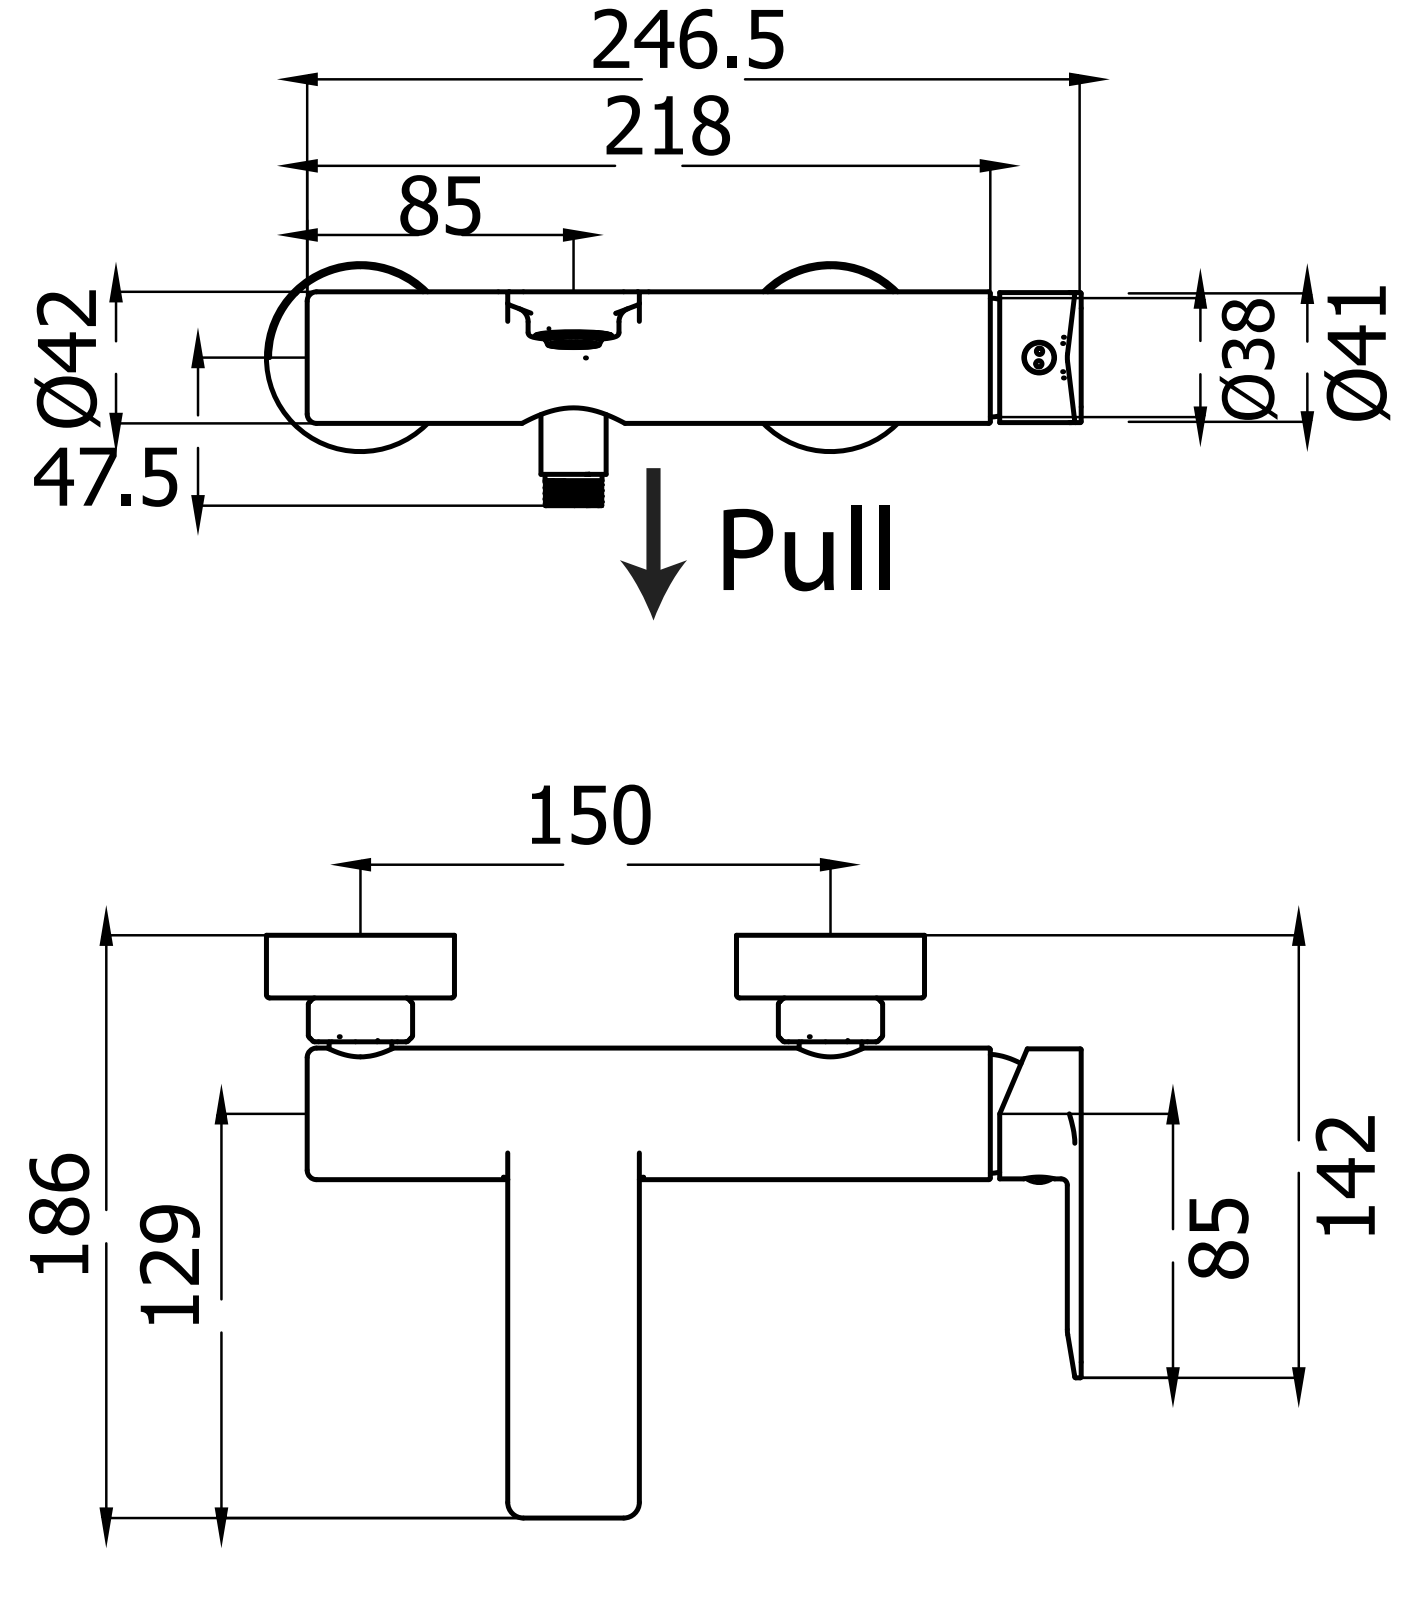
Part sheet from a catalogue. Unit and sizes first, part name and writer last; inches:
Units: inches
Overall size (bounding box): 10.217 × 7.323 × 3.042
Round holes (diameter × count): ⌀0.02 ×317, ⌀0.205 ×3, ⌀0.748 ×3, ⌀0.827 ×3, ⌀0.079 ×2, ⌀0.236 ×2, ⌀0.276 ×2, ⌀0.354 ×2, ⌀0.661 ×2, ⌀0.736 ×2, ⌀0.839 ×2, ⌀0.866 ×2
Round bosses / shafts (diameter × count): ⌀1.181 ×3, ⌀0.787 ×3, ⌀2.362 ×2, ⌀0.984 ×2, ⌀0.913 ×2, ⌀0.709 ×2, ⌀0.65 ×2, ⌀0.63 ×2
Partial cylindrical surfaces — rounded edges, fillets, slot ends (radius × count): R0.031 ×24, R0.146 ×24, R0.02 ×7, R0.012 ×6, R0.197 ×5, R0.11 ×3, R0.394 ×3, R0.079 ×2
Main face-to-face distances: 0.087, 0.039, 0.079, 0.591, 1.5, 1.413, 0.783, 1.539, 1.453, 0.669
Hole centre spacings: 0.303, 0.192, 0.066, 0.13, 0.063, 0.303, 0.1, 0.17
Volume: 8.83 in³ · Surface area: 251 in²
Bodies: 9 solids, 3723 faces (1991 planar, 1176 cylindrical, 556 other)
Part name (STEP PRODUCT): TOM2C788654AYIV_1; TOM2C788654AYIV_2; TOM2C788654AYIV_3; TOM2C788654AYIV_4 (+8 more)
STEP written by: CREO PARAMETRIC BY PTC INC, 2020281 (CONFIG_CONTROL_DESIGN)
